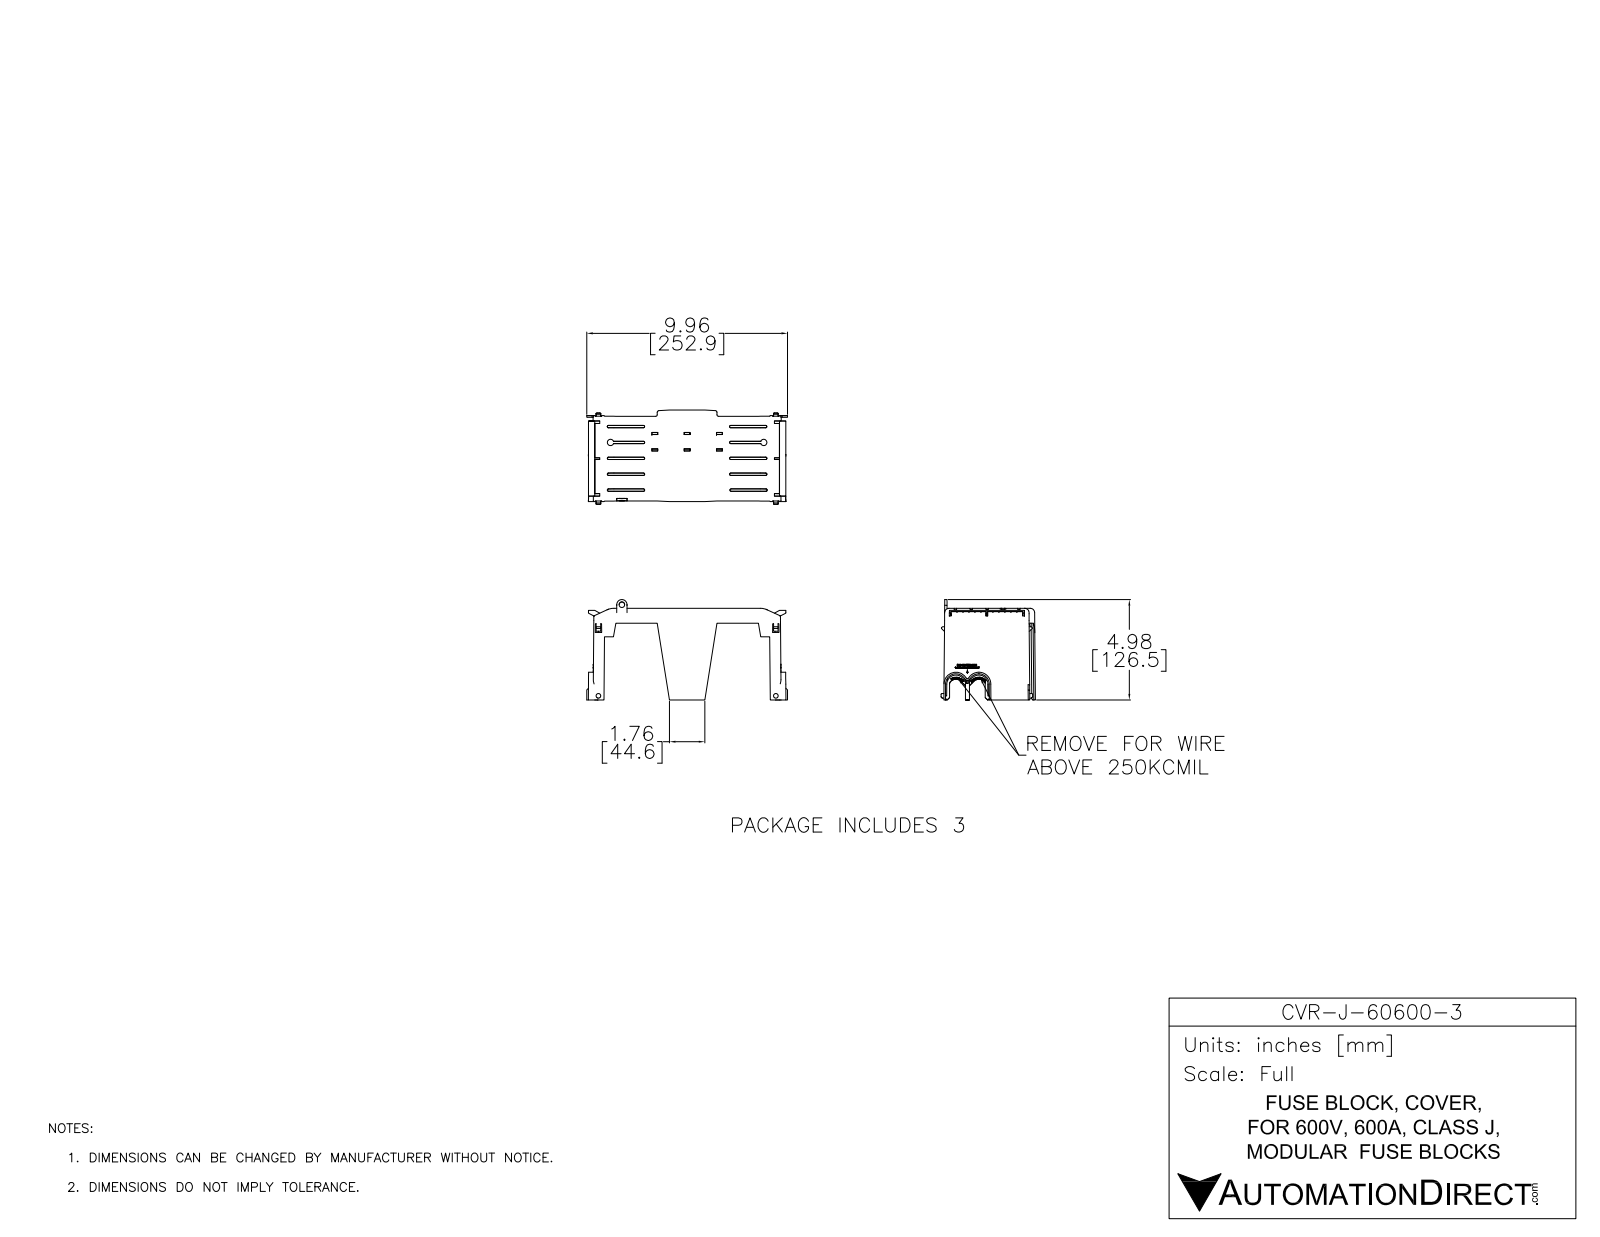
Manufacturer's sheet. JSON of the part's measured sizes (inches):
{"part_name": "CVR-J-60600-3", "step_written_by": "SolidWorks 2017 (AUTOMOTIVE_DESIGN)", "units": "inches", "bodies": {"solids": 1, "faces": 2344, "planar": 1597, "cylindrical": 167, "other": 580}, "overall_size": [9.959, 4.983, 4.677], "volume_in3": 10.27, "surface_area_in2": 271.3, "round_holes": [[0.276, 1]], "partial_cylinders_radius": [[0.039, 18], [0.118, 12], [0.028, 10], [0.217, 9], [0.138, 7], [0.079, 6], [0.354, 4], [0.512, 4]], "face_to_face_distances": [0.079, 0.079, 0.276, 0.197, 0.354, 0.803, 0.795, 0.118, 1.614, 0.158]}
